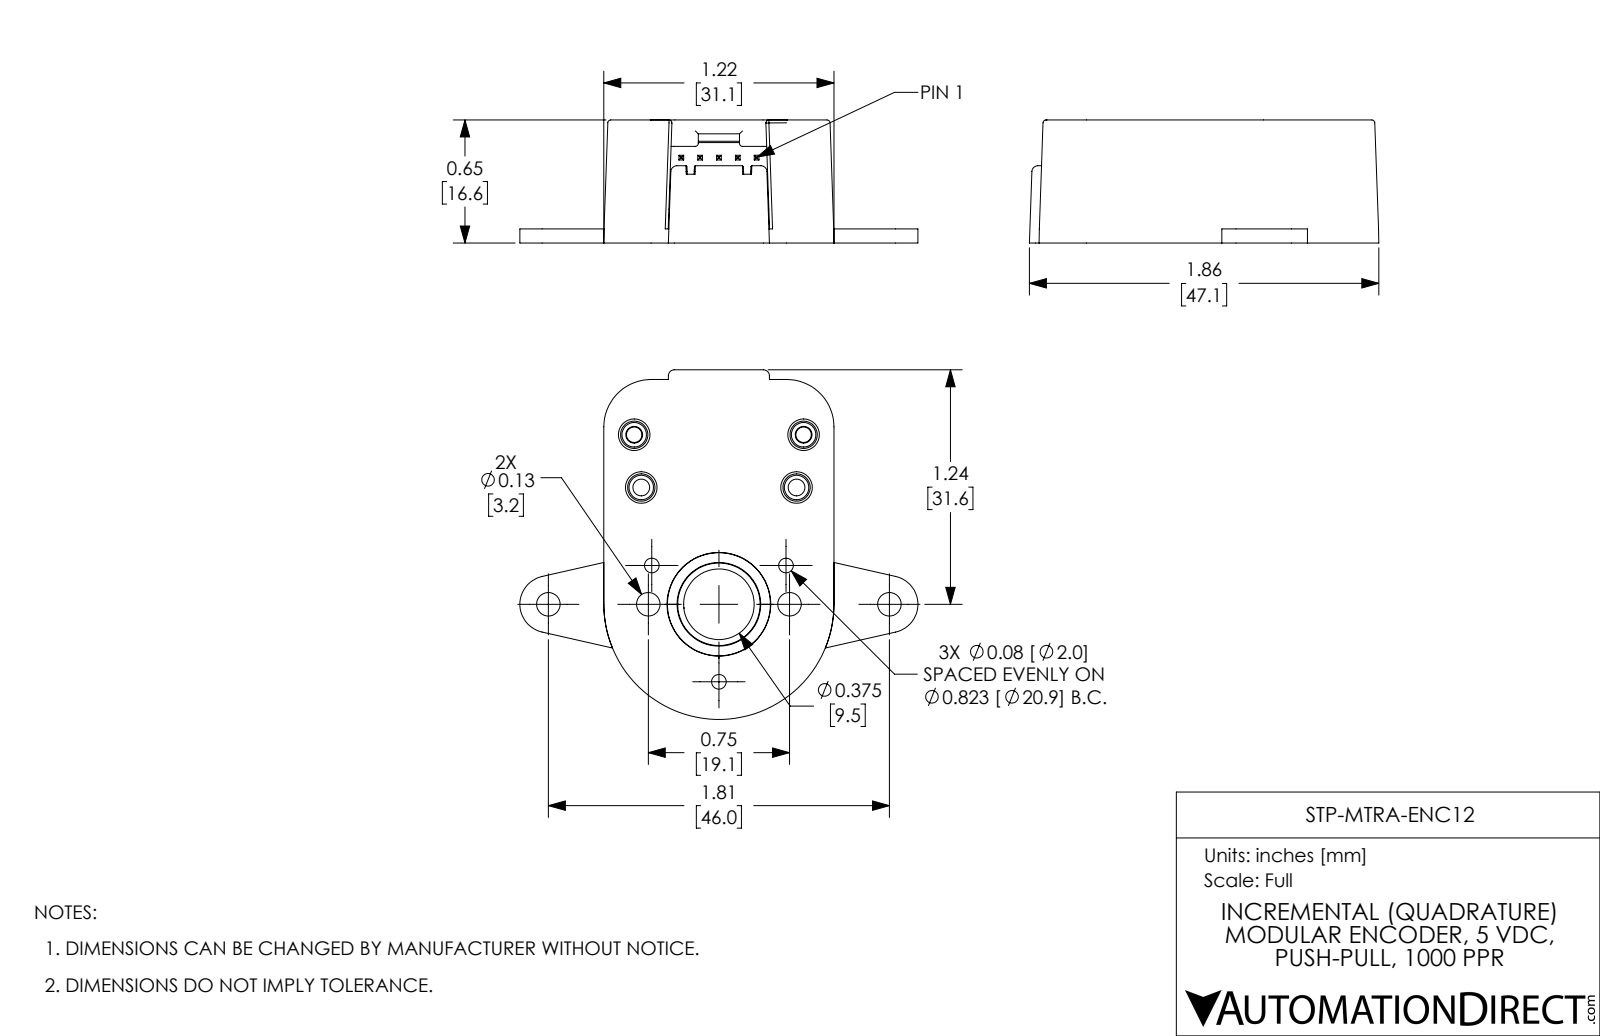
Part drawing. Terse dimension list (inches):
name: STP-MTRA-ENC12
written by: SolidWorks 2017 (AUTOMOTIVE_DESIGN)
unit: in
bodies: 13 solids, 1132 faces (410 planar, 288 cylindrical, 434 other)
size: 2.115 × 1.856 × 0.653
volume: 0.2 in³; area: 19.91 in²
holes: 4× ⌀0.089, 4× ⌀0.125, 3× ⌀0.078, 3× ⌀0.145, 2× ⌀0.095, 2× ⌀0.109, 1× ⌀0.093, 1× ⌀0.145, 1× ⌀0.375, 1× ⌀0.551
bosses: 4× ⌀0.187, 4× ⌀0.16, 3× ⌀0.112, 2× ⌀0.195, 1× ⌀0.52, 1× ⌀0.487, 1× ⌀0.096
rounds: 36× R0.016, 24× R0.031, 4× R0.01, 2× R0.047, 2× R0.047, 2× R0.048, 2× R0.075, 2× R0.095
face distances: 0.653, 0.135, 0.518, 0.405, 0.54, 0.113, 0.398, 0.458, 1.1, 0.533
hole spacings: 0.162, 0.207, 0.282, 0.411, 0.418, 0.531, 0.557, 0.587
